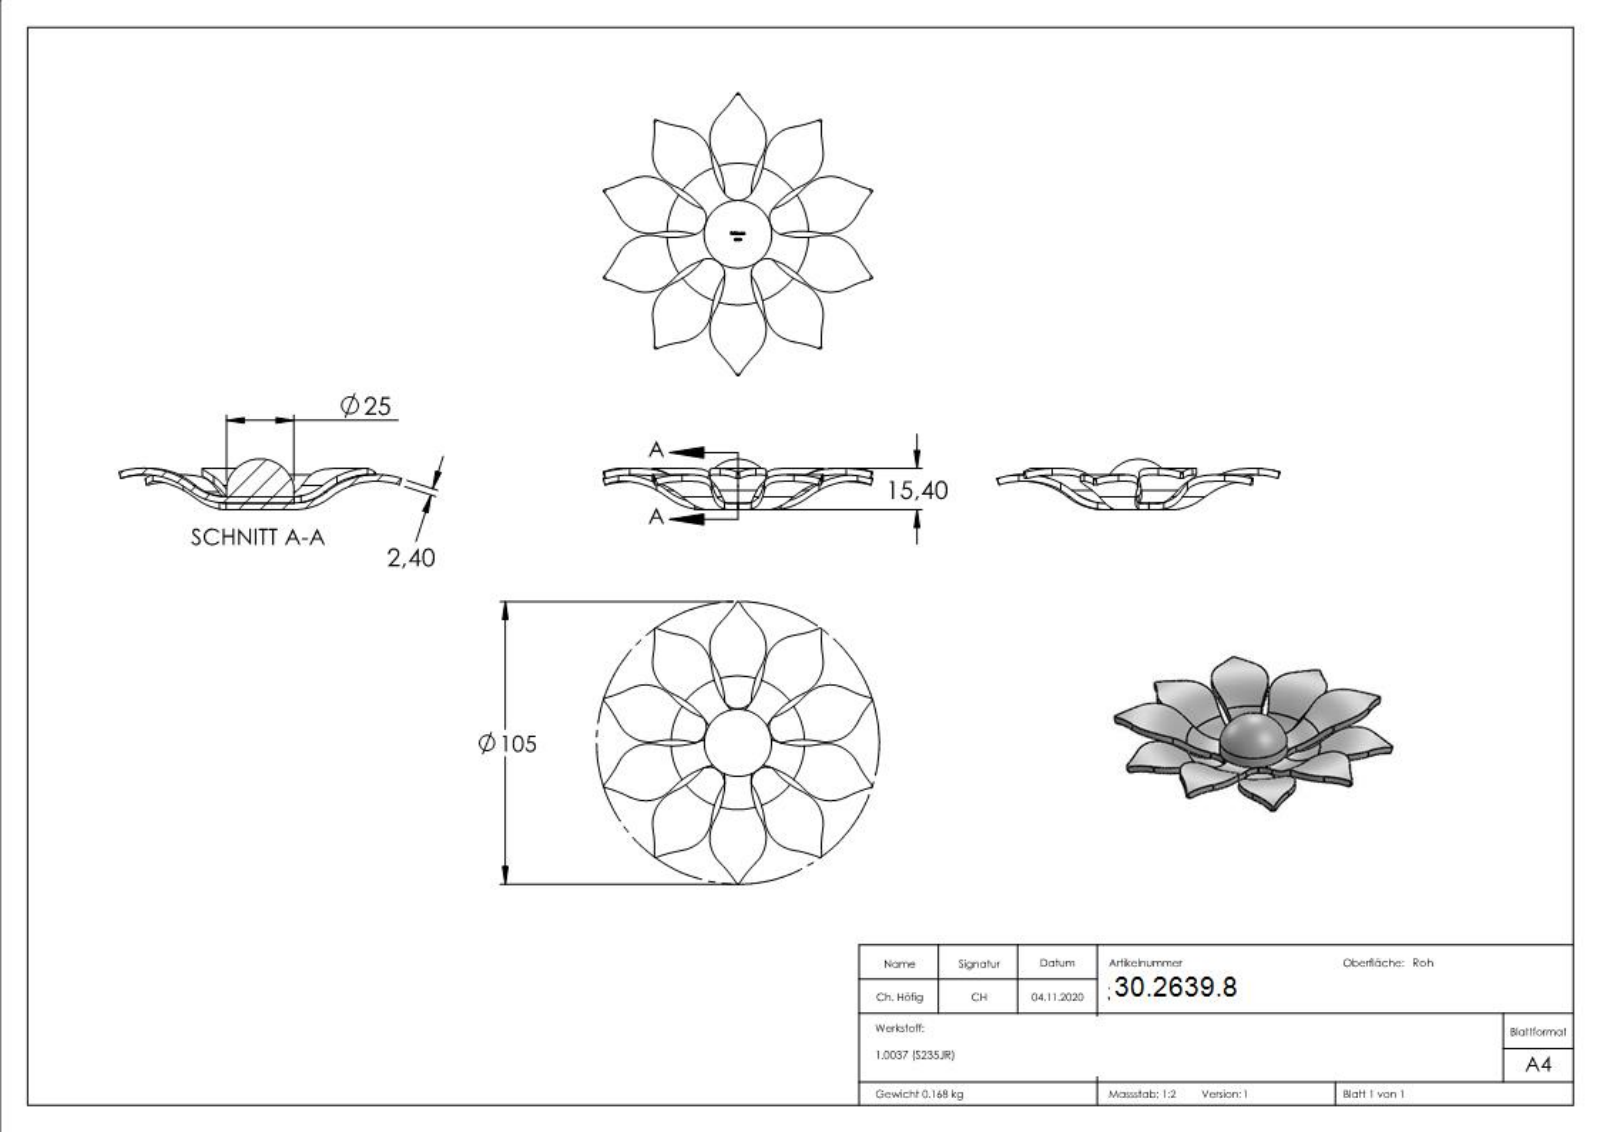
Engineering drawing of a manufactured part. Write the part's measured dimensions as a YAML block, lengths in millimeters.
part_name: "3263 Teil2; 3263 Teil1; 3263 Teil2_3263 Teil2; 3263"
step_written_by: "SolidWorks 2018 (CONFIG_CONTROL_DESIGN)"
units: millimeters
bodies: {solids: 3, faces: 383, planar: 90, cylindrical: 110, other: 183}
overall_size: [105, 99.91, 18.8]
volume: 21494
surface_area: 17808
round_bosses_or_shafts:
  - {diameter: 25.2, count: 1}
  - {diameter: 25, count: 1}
partial_cylinders:
  - {radius: 5.8, count: 20}
  - {radius: 13, count: 20}
  - {radius: 30, count: 20}
  - {radius: 45, count: 20}
  - {radius: 0.5, count: 10}
face_to_face_distances: [2.4, 4.8, 2.3, 4.7, 1.78, 0.44, 0.67, 0.83, 0.99, 1.21]
